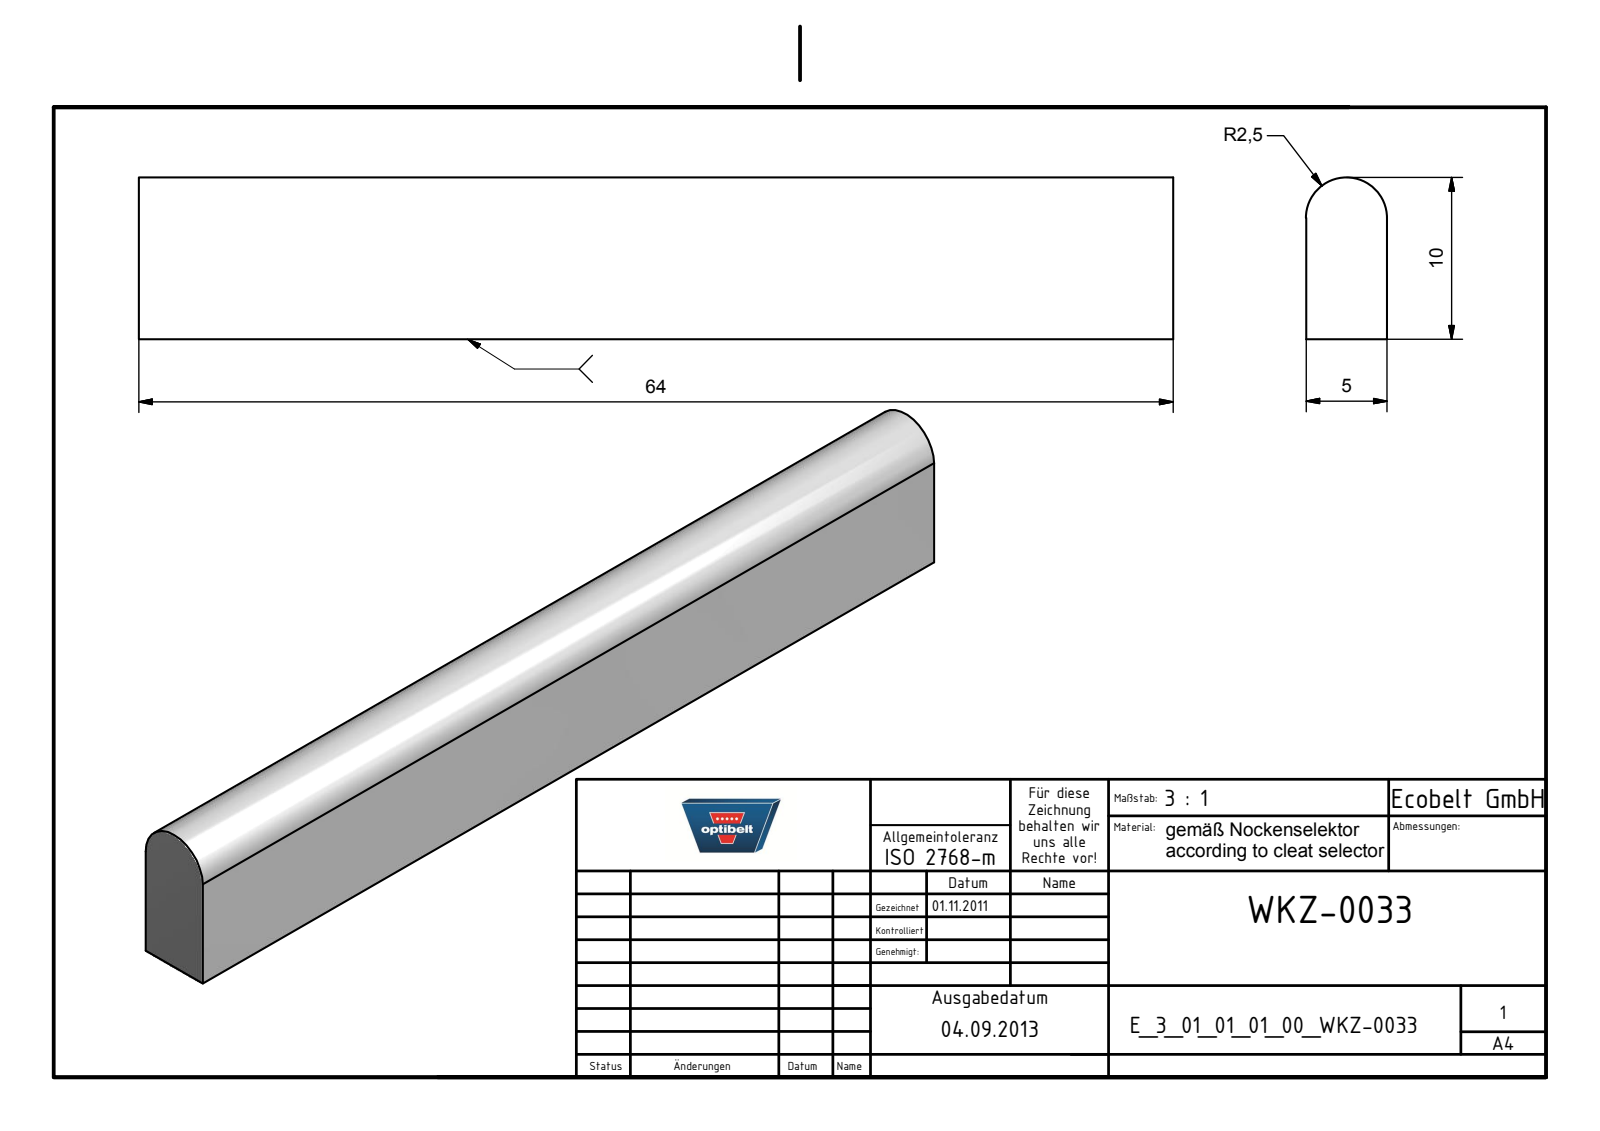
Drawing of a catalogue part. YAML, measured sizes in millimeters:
part_name: "E_3_01_01_01_00_WKZ-0033"
step_written_by: "Autodesk Inventor 2021 (AUTOMOTIVE_DESIGN)"
units: millimeters
bodies: {solids: 1, faces: 6, planar: 5, cylindrical: 1, other: 0}
overall_size: [64, 10, 5]
volume: 3028
surface_area: 1877
partial_cylinders:
  - {radius: 2.5, count: 1}
face_to_face_distances: [5, 64]
